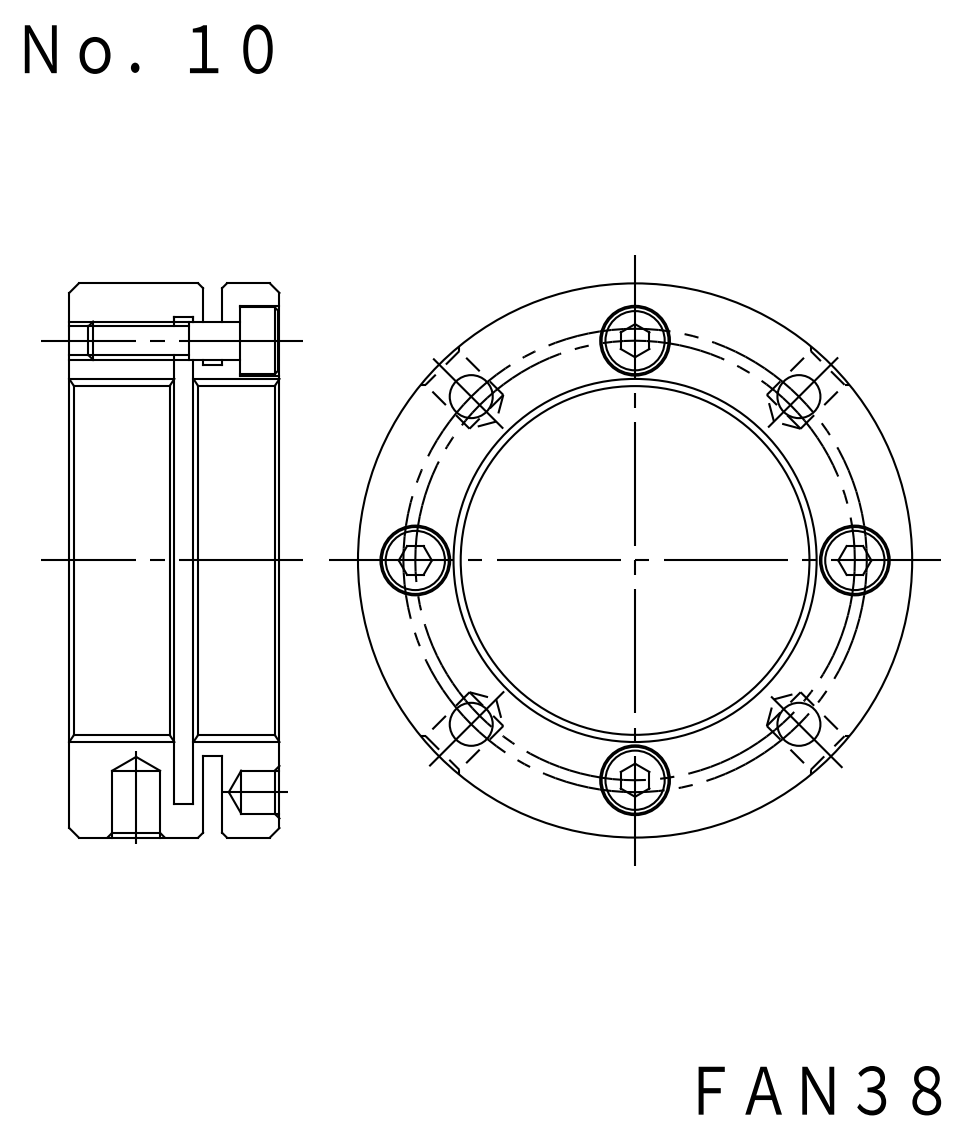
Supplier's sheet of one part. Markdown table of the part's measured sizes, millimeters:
| quantity | value |
| --- | --- |
| part name | FKD FAN38; M4X16_default |
| STEP written by | SolidWorks 2012 (CONFIG_CONTROL_DESIGN) |
| units | millimeters |
| bodies | 5 solids, 142 faces (50 planar, 76 cylindrical, 16 other) |
| overall size | 58 × 58 × 22 |
| volume | 27 978 mm³ |
| surface area | 17 046 mm² |
| round holes (diameter × count) | 3.24 × 4, 4.3 × 4, 4.5 × 4, 5 × 4, 7.3 × 4, 38 × 1, 54 × 1 |
| round bosses / shafts (diameter × count) | 7 × 4, 4 × 4, 58 × 1, 44 × 1 |
| main face-to-face distances | 11, 2, 3, 22, 16, 13, 9, 14, 1, 8 |
| hole center spacings | 18.66, 45.04, 24.25, 24.5, 34.3, 34.65, 48.51, 49 |
